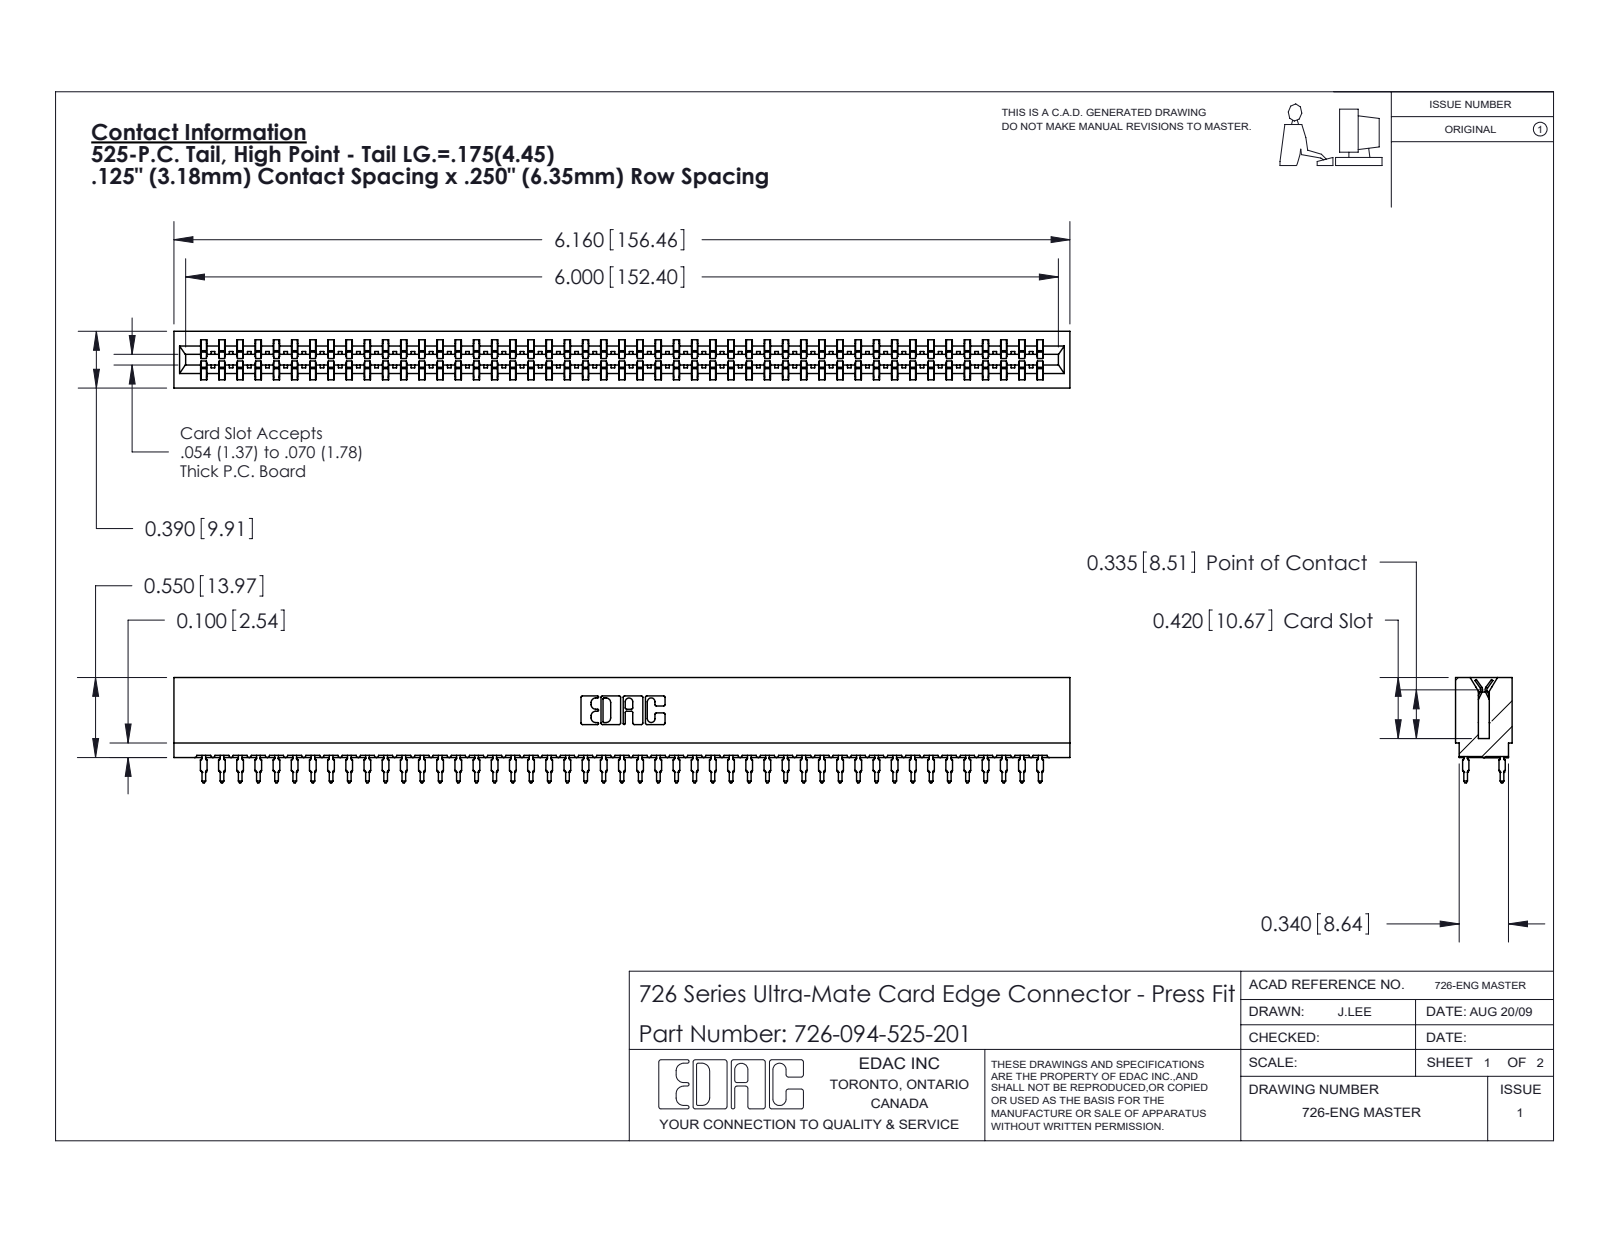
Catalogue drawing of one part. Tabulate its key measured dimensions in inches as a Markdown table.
| quantity | value |
| --- | --- |
| part name | 726 Part_.515 Slot Depth - 01; 746-292-001_525; 726-094-525-201 |
| STEP written by | SolidWorks 2020 (CONFIG_CONTROL_DESIGN) |
| units | inches |
| bodies | 95 solids, 8510 faces (4379 planar, 1687 cylindrical, 2444 other) |
| overall size | 6.16 × 0.724 × 0.39 |
| volume | 0.874 in³ |
| surface area | 36.81 in² |
| partial cylindrical surfaces (radius × count) | 0.021 × 188, 0.015 × 48, 0.01 × 22, 0.005 × 8, 0.011 × 8, 0.007 × 6, 0.031 × 6, 0.026 × 3 |
| main face-to-face distances | 0.057, 0.333, 0.39, 0.025, 0.307, 0.25, 0.275, 0.083, 0.365, 0.032 |
